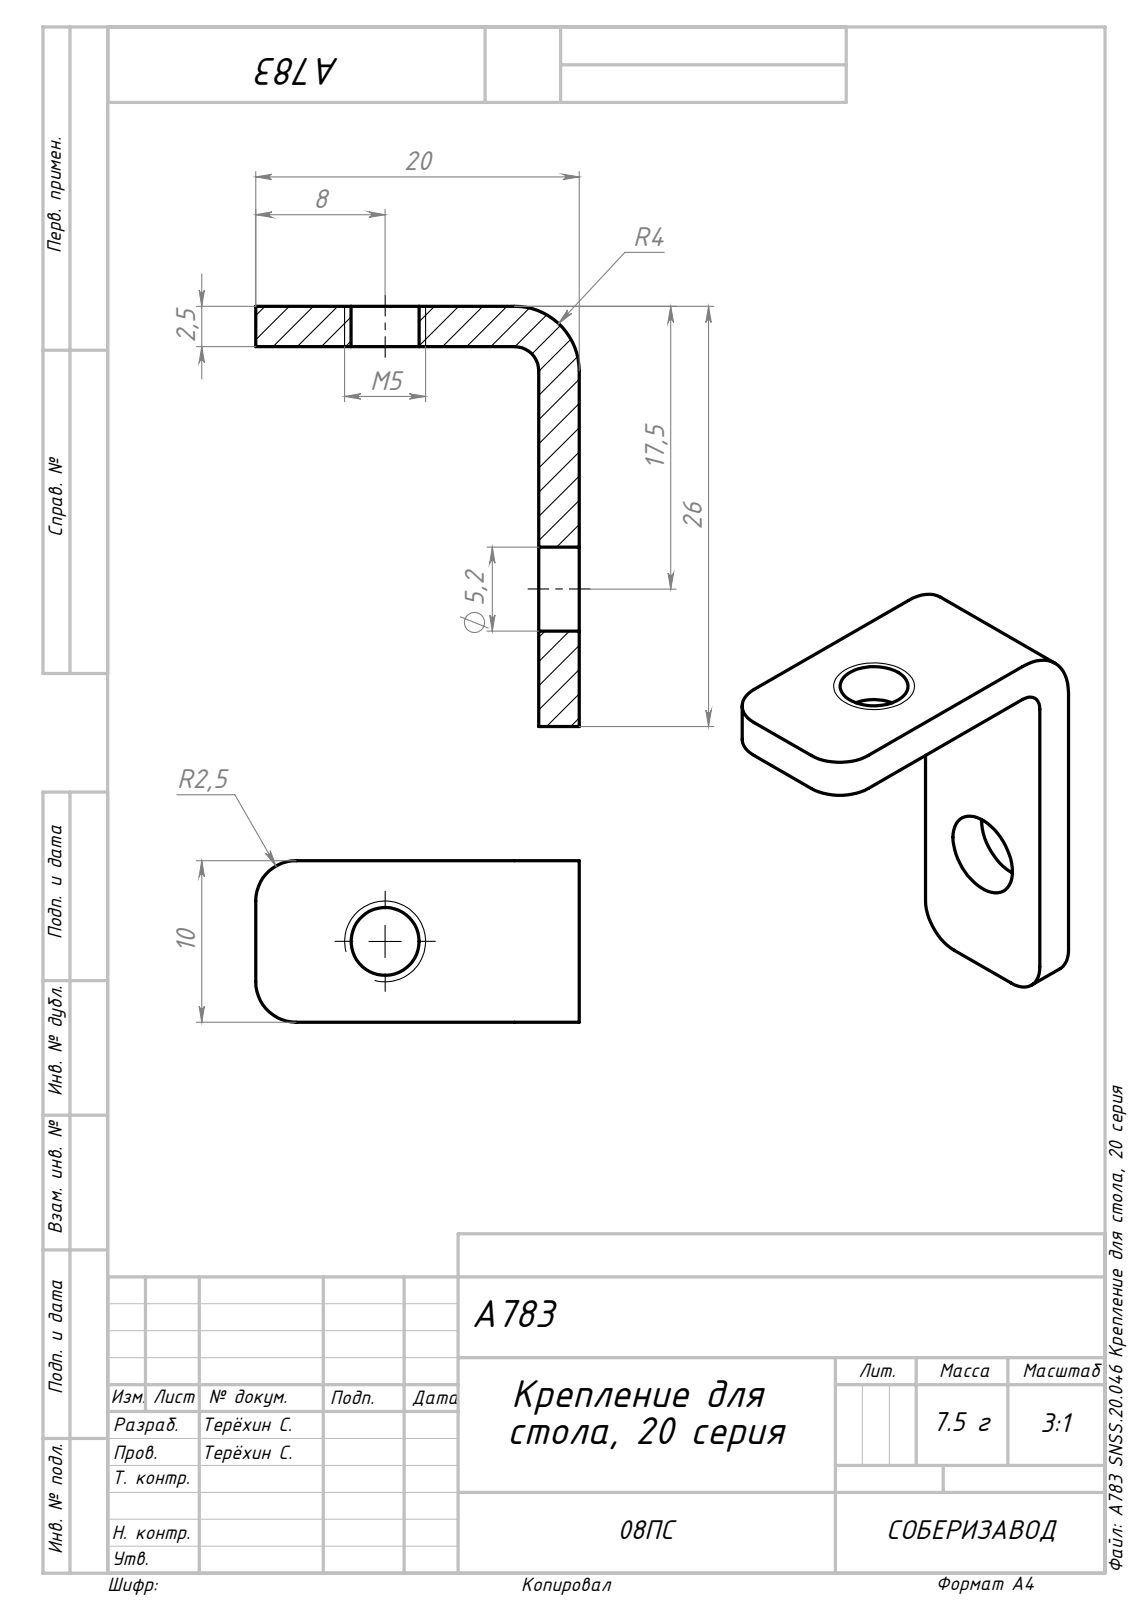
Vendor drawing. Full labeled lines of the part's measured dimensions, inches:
Part name (STEP PRODUCT): A783 SNSS.20.046 Крепление для стола, 20 серия
STEP written by: SolidWorks 2022 (AUTOMOTIVE_DESIGN)
Units: inches
Bodies: 1 solid, 22 faces (12 planar, 10 cylindrical, 0 other)
Overall size (bounding box): 1.024 × 0.787 × 0.394
Volume: 0.058 in³ · Surface area: 1.69 in²
Round holes (diameter × count): ⌀0.165 ×1, ⌀0.205 ×1
Partial cylindrical surfaces — rounded edges, fillets, slot ends (radius × count): R0.098 ×4, R0.059 ×1, R0.157 ×1
Main face-to-face distances: 0.098, 0.394, 0.925, 1.024, 0.689, 0.787
